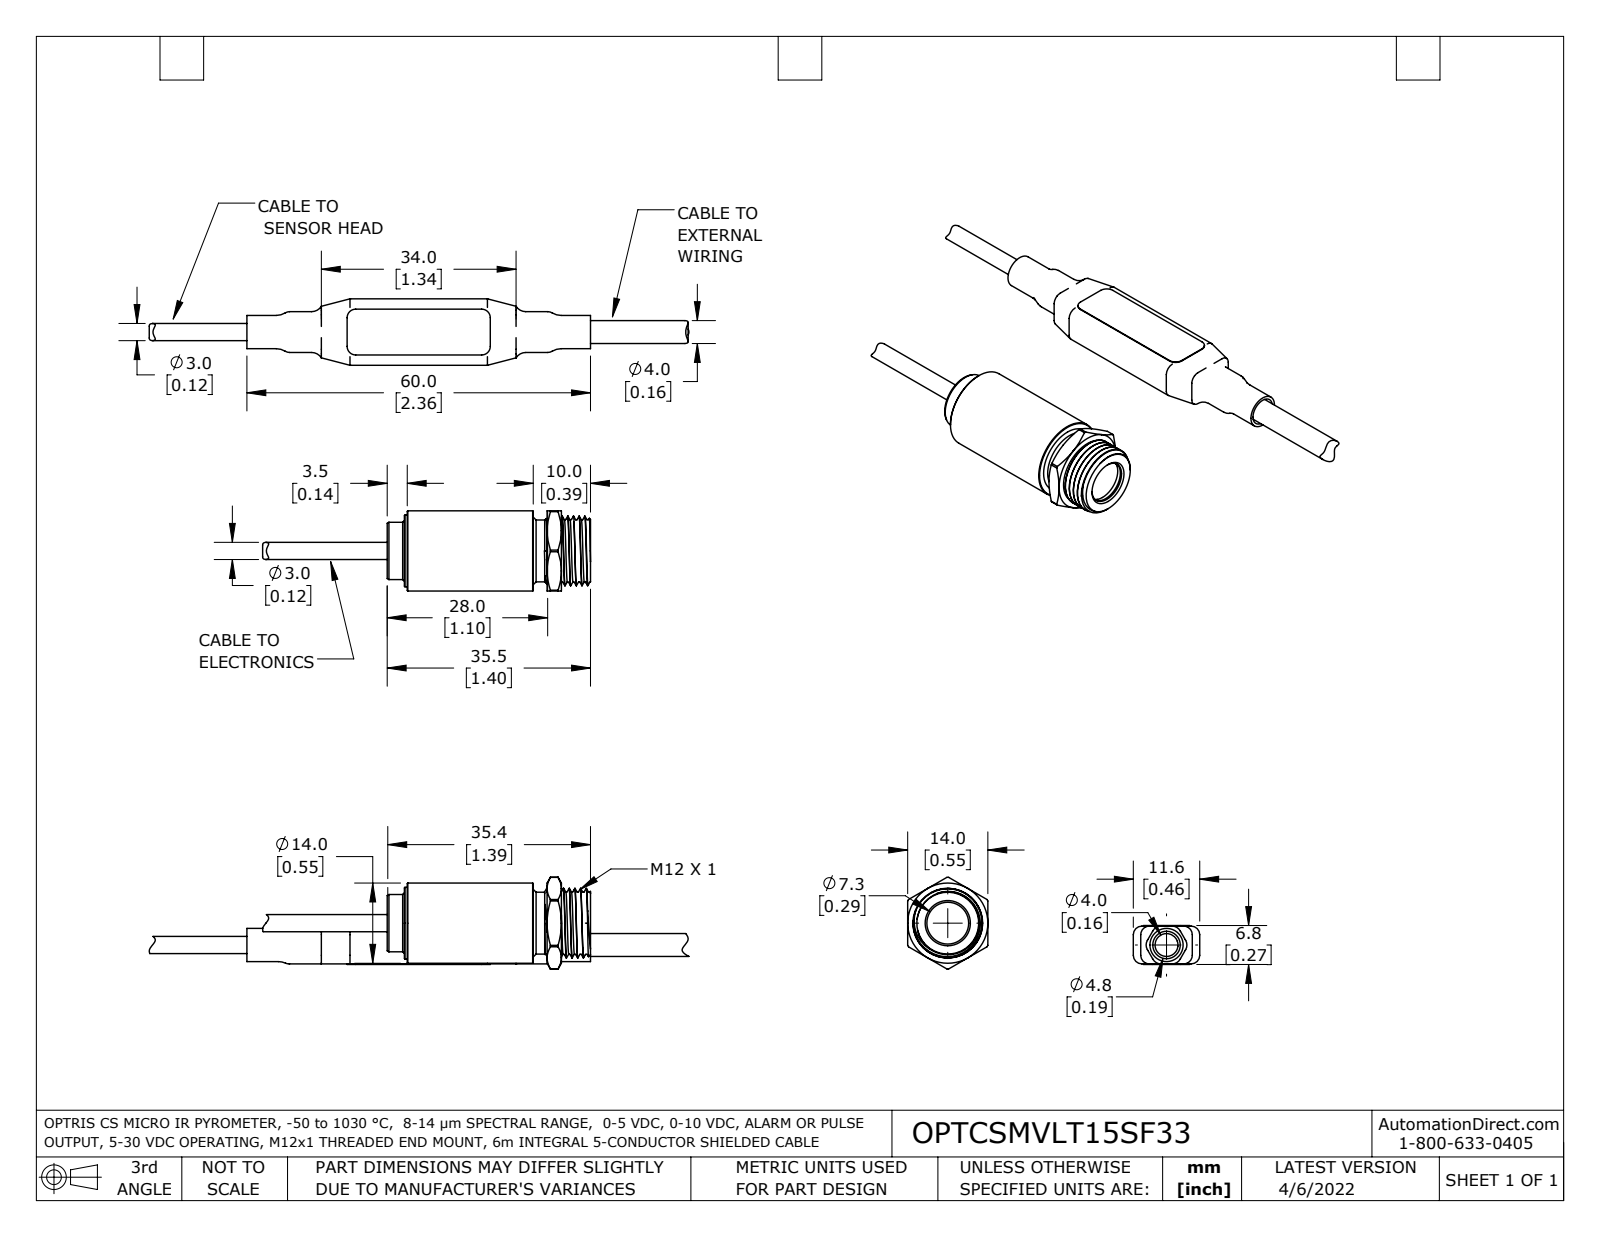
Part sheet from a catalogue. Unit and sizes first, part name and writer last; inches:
Units: inches
Overall size (bounding box): 3.71 × 2.008 × 0.63
Round holes (diameter × count): ⌀0.047 ×2, ⌀0.118 ×2, ⌀0.126 ×1, ⌀0.181 ×1, ⌀0.189 ×1, ⌀0.287 ×1, ⌀0.378 ×1, ⌀0.394 ×1, ⌀0.425 ×1, ⌀0.453 ×1, ⌀0.488 ×1, ⌀0.496 ×1
Round bosses / shafts (diameter × count): ⌀0.031 ×10, ⌀0.035 ×8, ⌀0.02 ×4, ⌀0.551 ×1, ⌀0.492 ×1, ⌀0.472 ×1, ⌀0.433 ×1, ⌀0.315 ×1
Partial cylindrical surfaces — rounded edges, fillets, slot ends (radius × count): R0.059 ×8, R0.043 ×6, R0.063 ×6, R0.039 ×4, R0.016 ×2, R0.047 ×1, R0.315 ×1
Main face-to-face distances: 0.02, 0.24, 0.26, 0.024, 0.244, 0.264, 0.22, 0.268, 0.437, 0.098
Hole centre spacings: 0.157, 0.315, 1.504, 1.511, 1.535
Volume: 0.222 in³ · Surface area: 16.56 in²
Bodies: 14 solids, 591 faces (97 planar, 179 cylindrical, 315 other)
Part name (STEP PRODUCT): OPTCSM... - Sensing Head + Electronics WITH Mov sensor1 No TB nc fxt
STEP written by: SolidWorks 2021 (AUTOMOTIVE_DESIGN)
